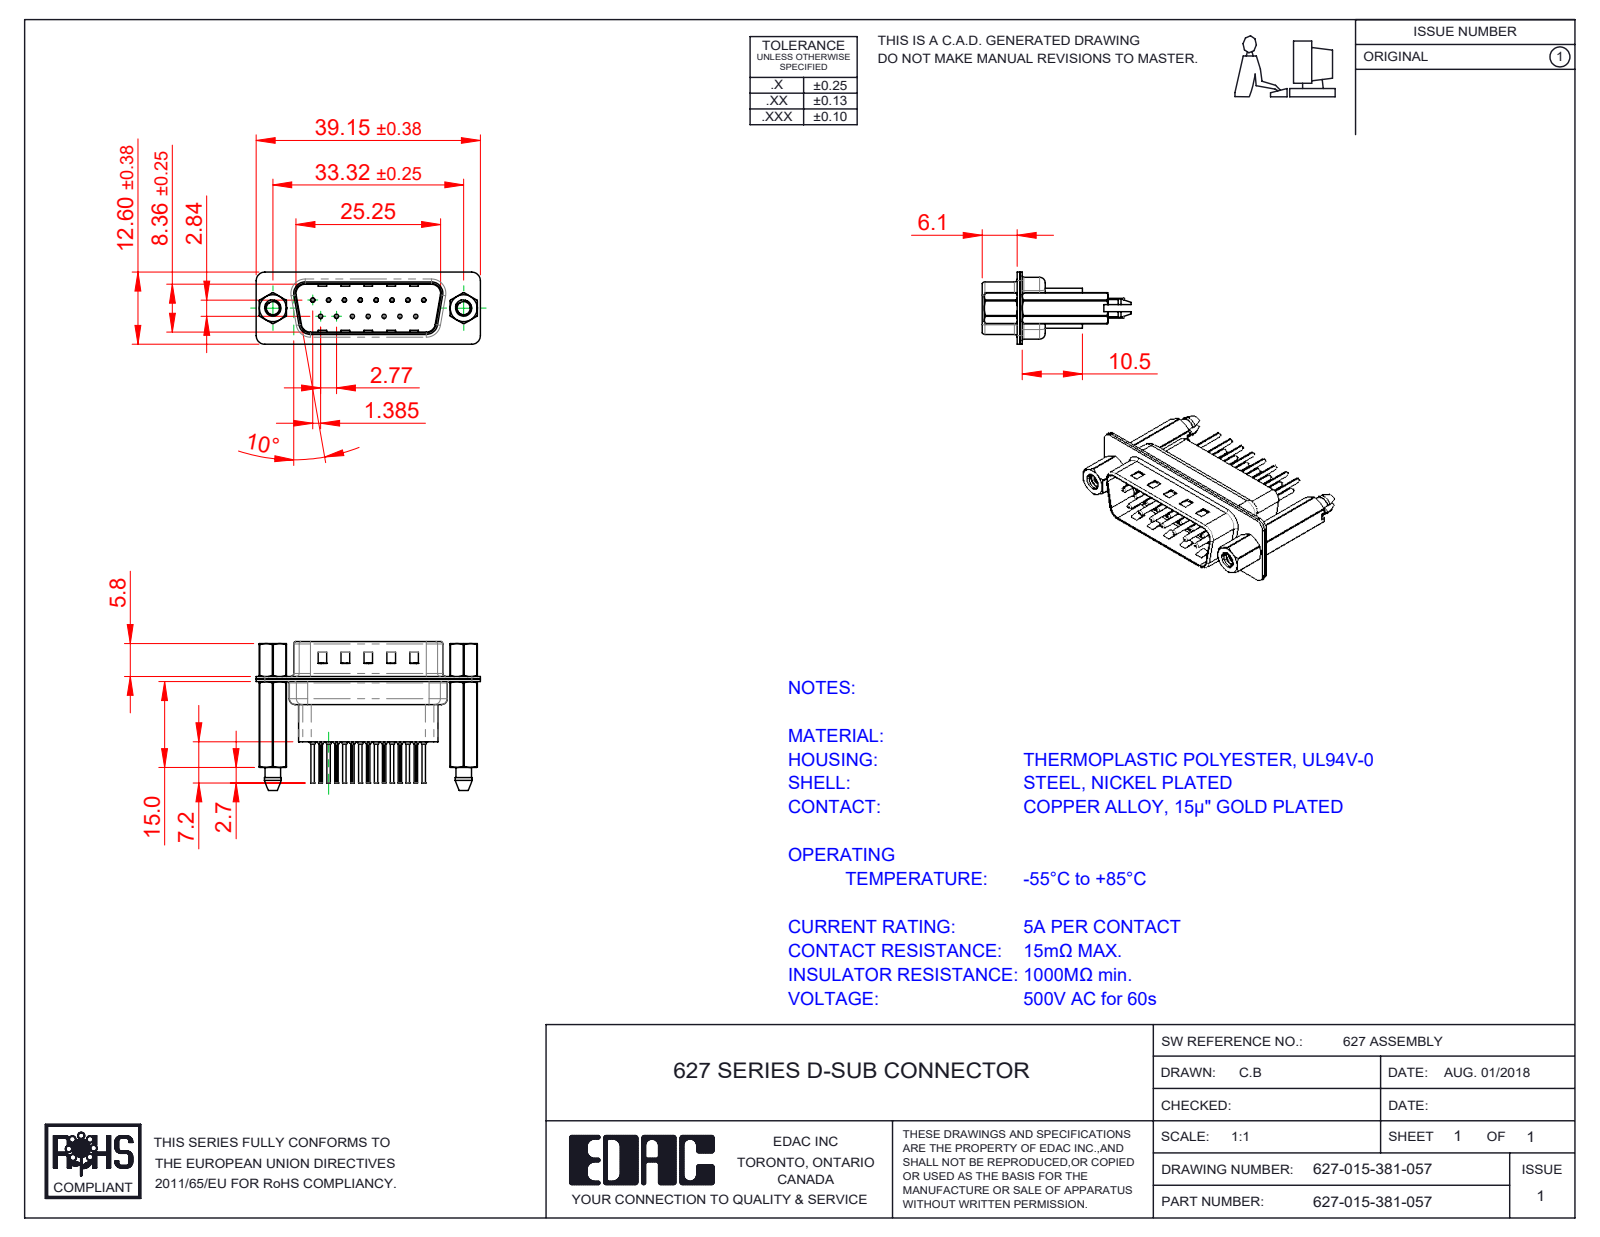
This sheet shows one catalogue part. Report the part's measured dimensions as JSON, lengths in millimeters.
{"part_name": "627 Contact Row 2_61; 627 Housing_15 HP; 627 4-40 Hex Standoff; 627 Shell Rear_15 Contacts (+4 more)", "step_written_by": "SolidWorks 2020 (CONFIG_CONTROL_DESIGN)", "units": "millimeters", "bodies": {"solids": 22, "faces": 2044, "planar": 553, "cylindrical": 826, "other": 665}, "overall_size": [39.15, 25.9, 12.6], "volume_mm3": 3148, "surface_area_mm2": 8038, "round_holes": [[0.2, 15], [0.35, 15], [1.1, 15], [1.6, 15], [2.26, 2], [2.29, 2], [4, 2], [4.8, 2]], "round_bosses_or_shafts": [[2, 15], [1.5, 15], [0.75, 15], [0.6, 15], [4.9, 2], [2.79, 2]], "partial_cylinders_radius": [[0.1, 30], [1.5, 18], [2, 12], [1.6, 10], [0.5, 8], [0.25, 4], [0.6, 4], [0.65, 4]], "face_to_face_distances": [0.4, 0.45, 4.76, 0.9, 0.82, 9.58, 1.5, 16.66, 0.68, 7.68], "hole_center_spacings": [3.16, 2.77, 5.54, 8.31, 11.08, 5.03, 5.04, 7.48]}
